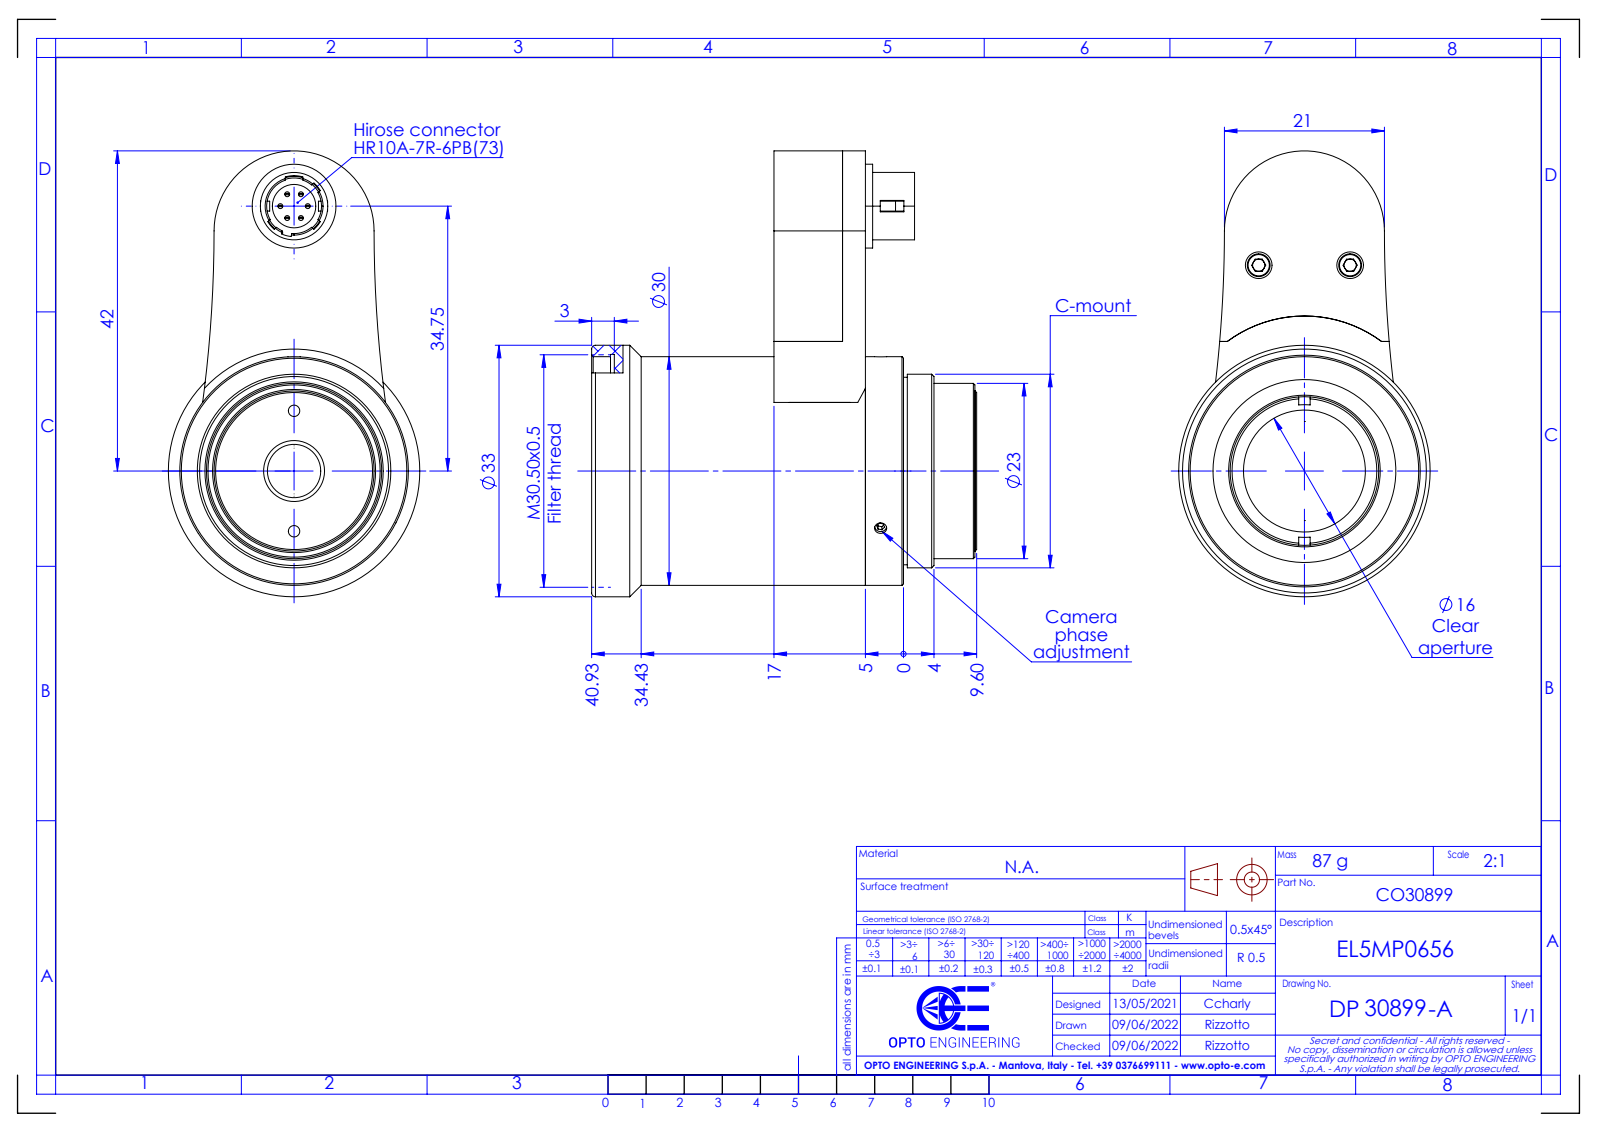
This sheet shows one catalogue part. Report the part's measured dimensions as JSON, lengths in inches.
{"part_name": "DP30899-A_EL5MP0656", "step_written_by": "SolidWorks 2021 (CONFIG_CONTROL_DESIGN)", "units": "inches", "bodies": {"solids": 0, "faces": 216, "planar": 84, "cylindrical": 84, "other": 48}, "overall_size": [2.303, 1.989, 1.299], "round_holes": [[0.063, 3], [0.059, 2], [0.138, 2], [0.276, 1], [0.291, 1], [0.63, 1], [0.768, 1], [1.205, 1]], "round_bosses_or_shafts": [[0.047, 2], [1.299, 1], [1.181, 1], [1, 1], [0.969, 1], [0.945, 1], [0.906, 1], [0.827, 1]], "partial_cylinders_radius": [[0.016, 2], [6.673, 2], [0.142, 1], [0.154, 1], [0.157, 1], [0.413, 1], [0.669, 1]], "face_to_face_distances": [0.472, 0.825, 1.298, 1.872, 1.047, 0.575, 1.494, 0.669, 0.197, 0.378], "hole_center_spacings": [0.311, 0.386, 0.788, 1.089, 1.394, 0.472, 0.622, 1.057]}
